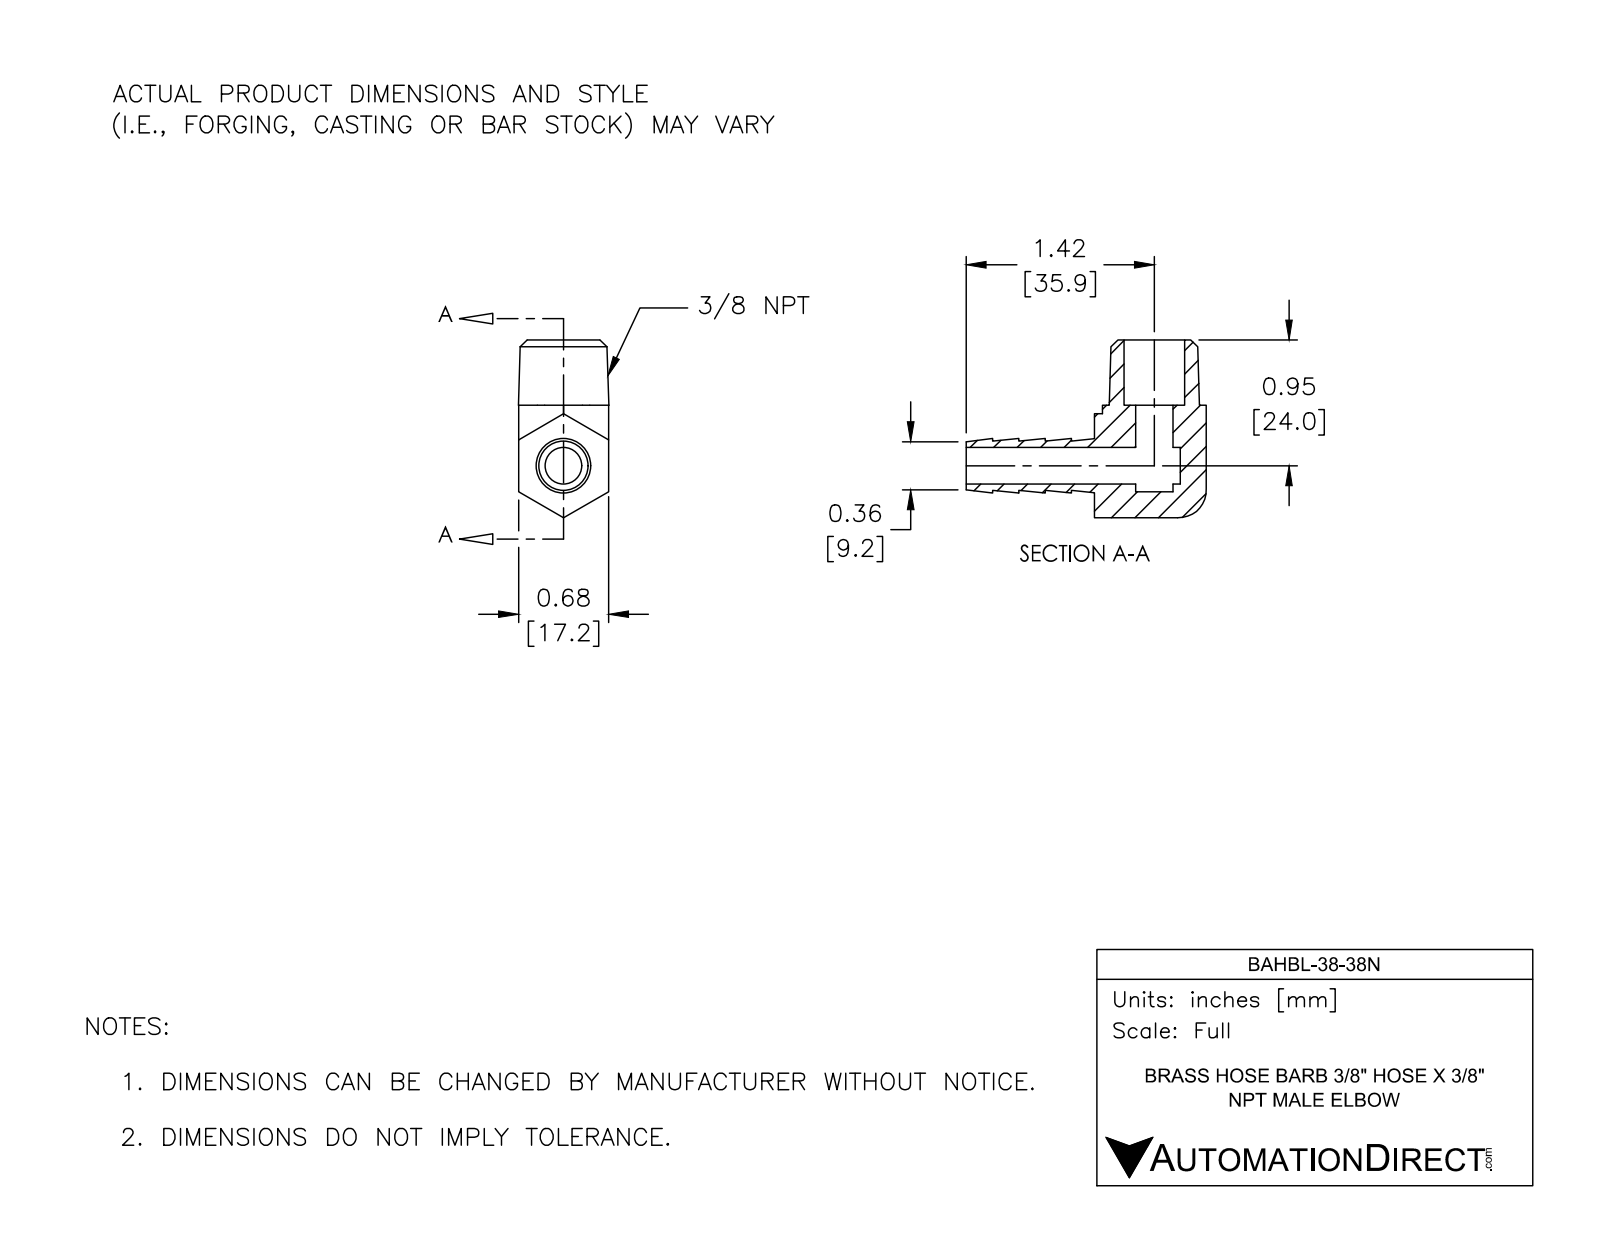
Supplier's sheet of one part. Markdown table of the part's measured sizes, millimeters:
| quantity | value |
| --- | --- |
| part name | BAHBL-38-38N |
| STEP written by | SolidWorks 2017 (AUTOMOTIVE_DESIGN) |
| units | millimeters |
| bodies | 1 solid, 56 faces (32 planar, 10 cylindrical, 14 other) |
| overall size | 45.9 × 34 × 17.3 |
| volume | 7 140 mm³ |
| surface area | 4 779 mm² |
| round holes (diameter × count) | 7 × 1, 7.1 × 1, 11.6 × 1 |
| partial cylindrical surfaces (radius × count) | 6.4 × 2 |
| main face-to-face distances | 17.2, 5, 12.4, 16.6, 29, 16.4, 10.1, 40.9, 24.5, 20.8 |
